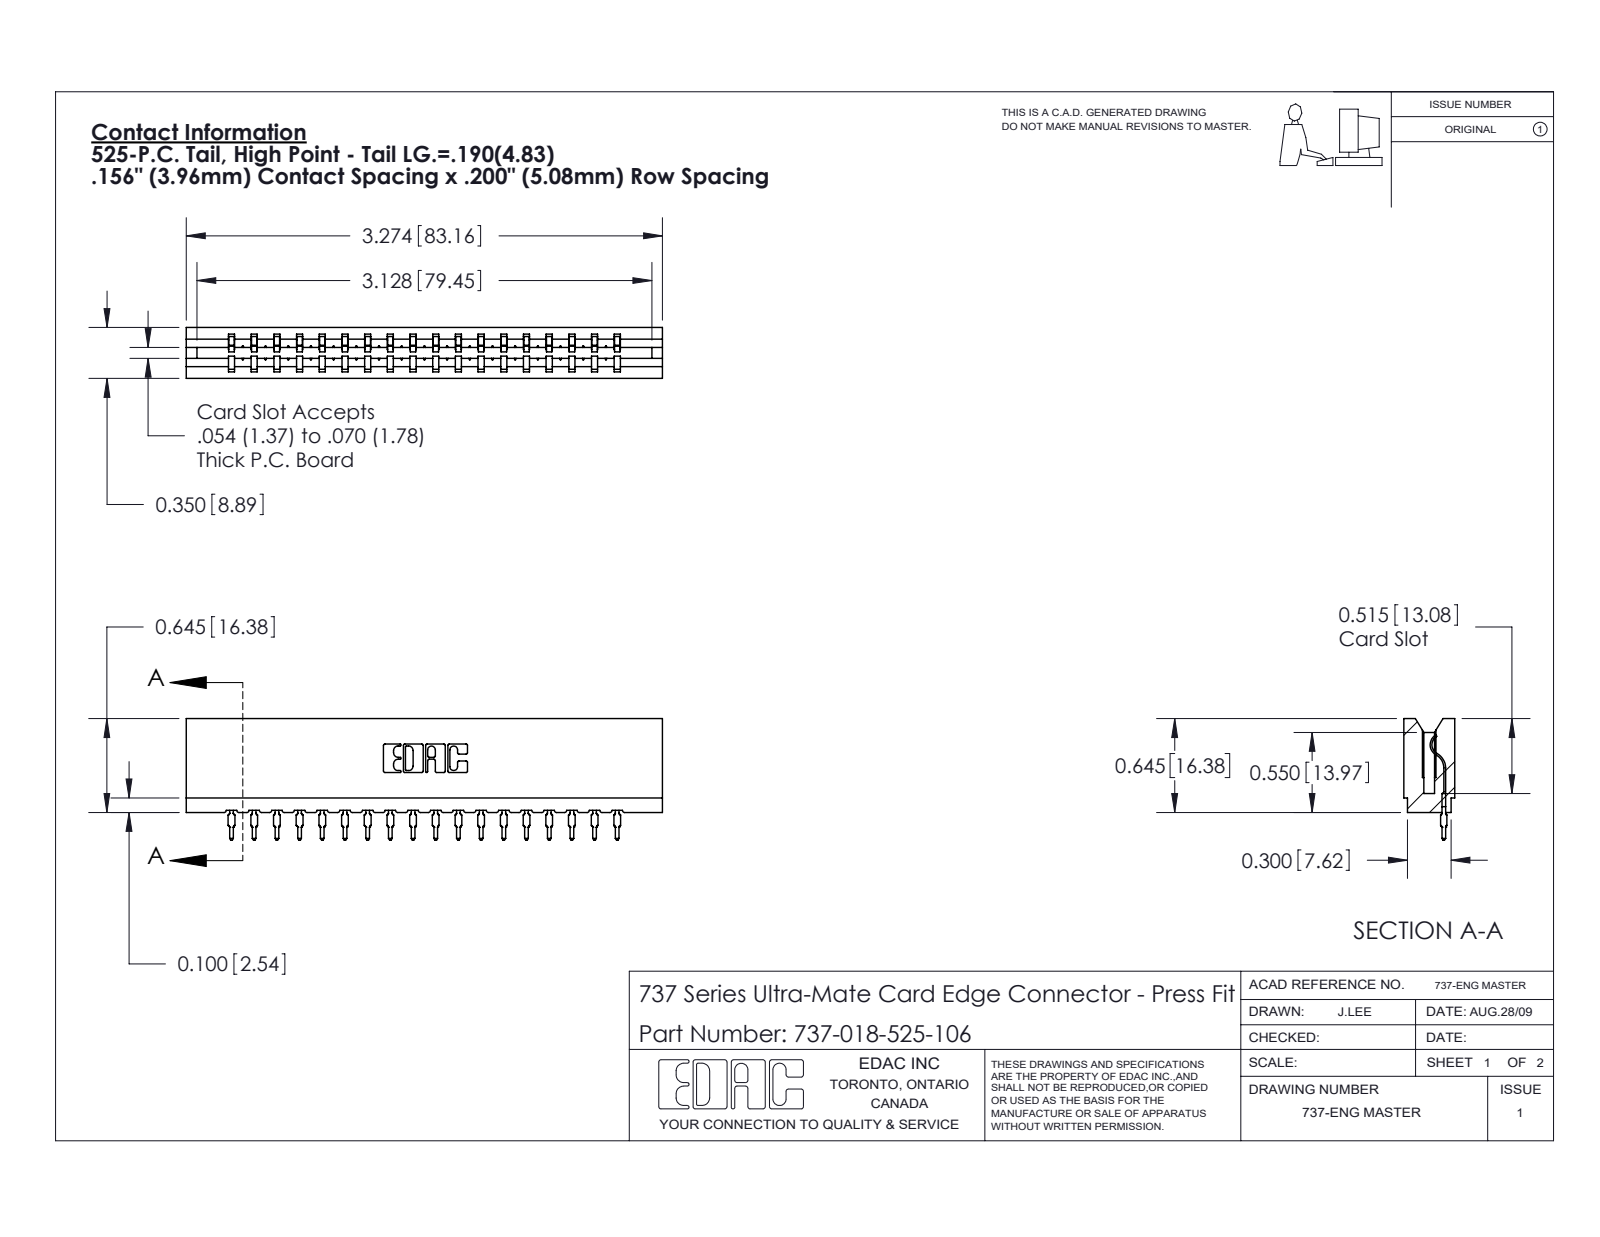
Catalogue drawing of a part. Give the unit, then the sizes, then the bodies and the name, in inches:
Units: inches
Overall size (bounding box): 3.274 × 0.836 × 0.35
Partial cylindrical surfaces — rounded edges, fillets, slot ends (radius × count): R0.015 ×36, R0.021 ×36, R0.01 ×22, R0.007 ×6, R0.031 ×6, R0.005 ×4, R0.011 ×4, R0.026 ×3
Main face-to-face distances: 0.138, 0.212, 0.35, 0.156, 0.624, 0.78, 0.468, 0.312, 1.404, 0.074
Volume: 0.499 in³ · Surface area: 16.26 in²
Bodies: 19 solids, 2129 faces (1279 planar, 382 cylindrical, 468 other)
Part name (STEP PRODUCT): 745-292-001_525; 737-018-525-106; 737 Part_Insulator Option - 06
STEP written by: SolidWorks 2020 (CONFIG_CONTROL_DESIGN)
